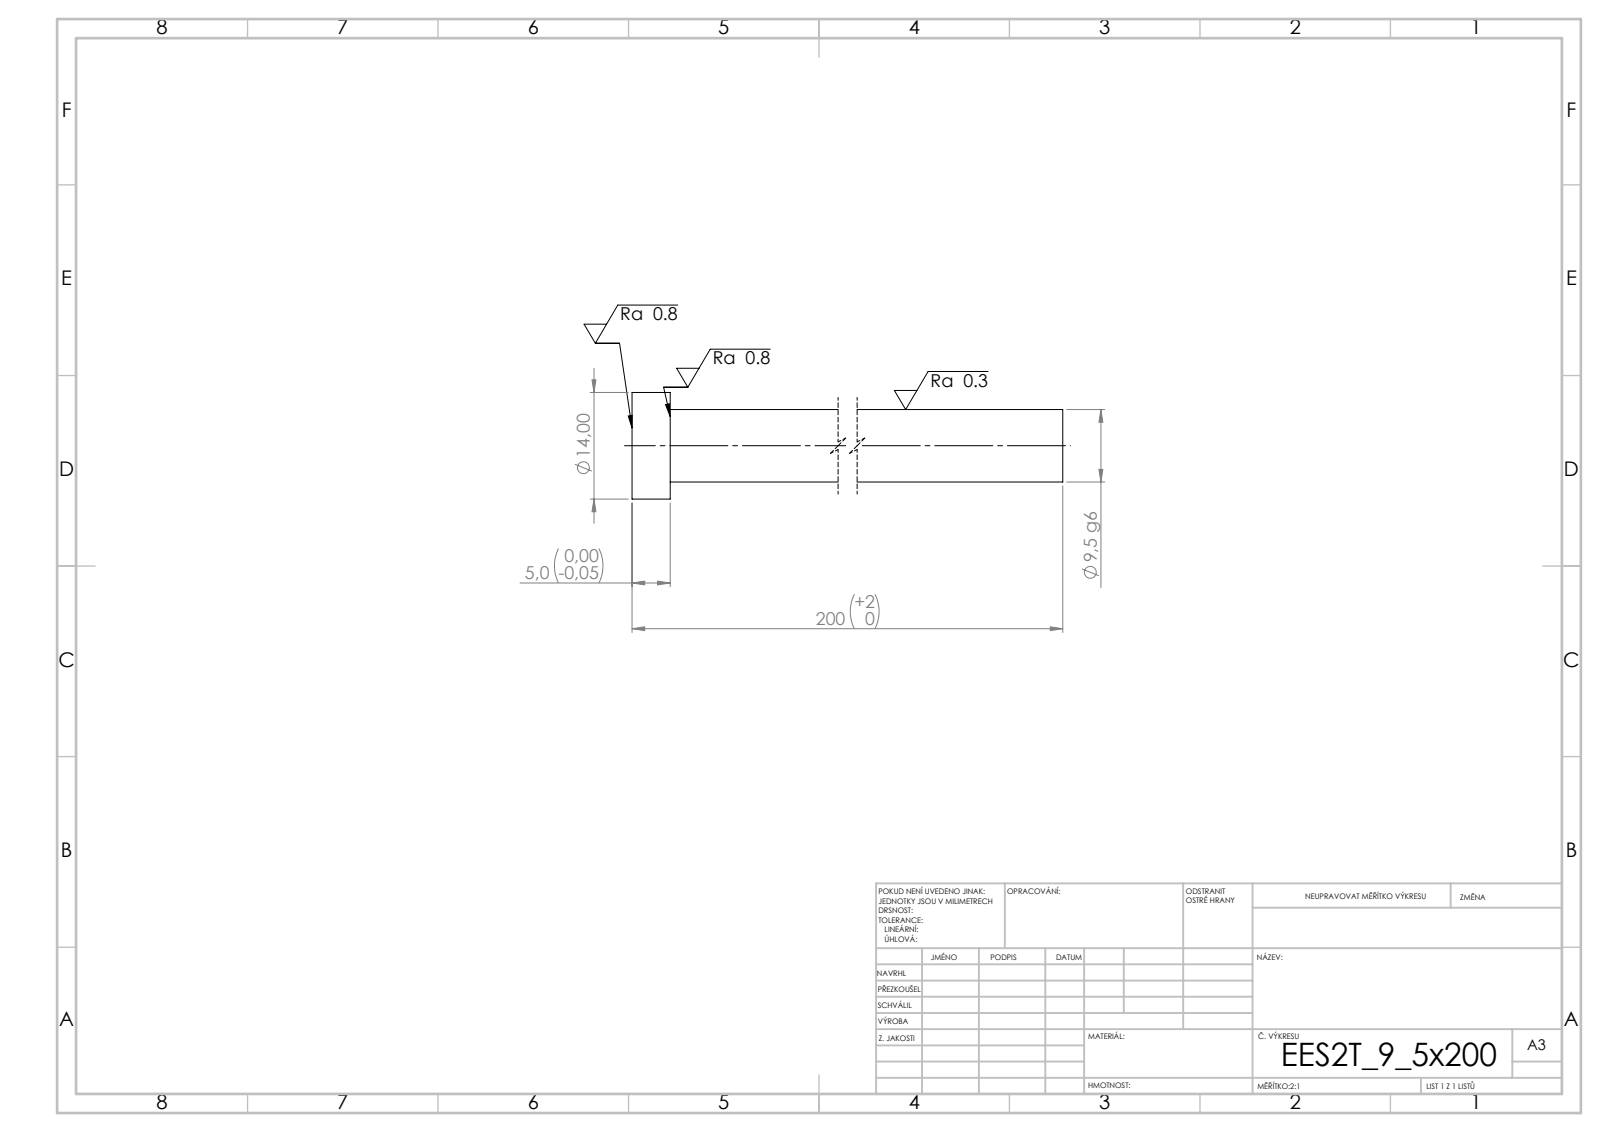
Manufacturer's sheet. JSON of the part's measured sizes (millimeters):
{"step_written_by": "SolidWorks 2019 (CONFIG_CONTROL_DESIGN)", "units": "millimeters", "bodies": {"solids": 1, "faces": 7, "planar": 3, "cylindrical": 4, "other": 0}, "overall_size": [200, 14, 14], "volume_mm3": 14592, "surface_area_mm2": 6348, "round_bosses_or_shafts": [[14, 1], [9.5, 1]], "face_to_face_distances": [5, 200, 195]}
